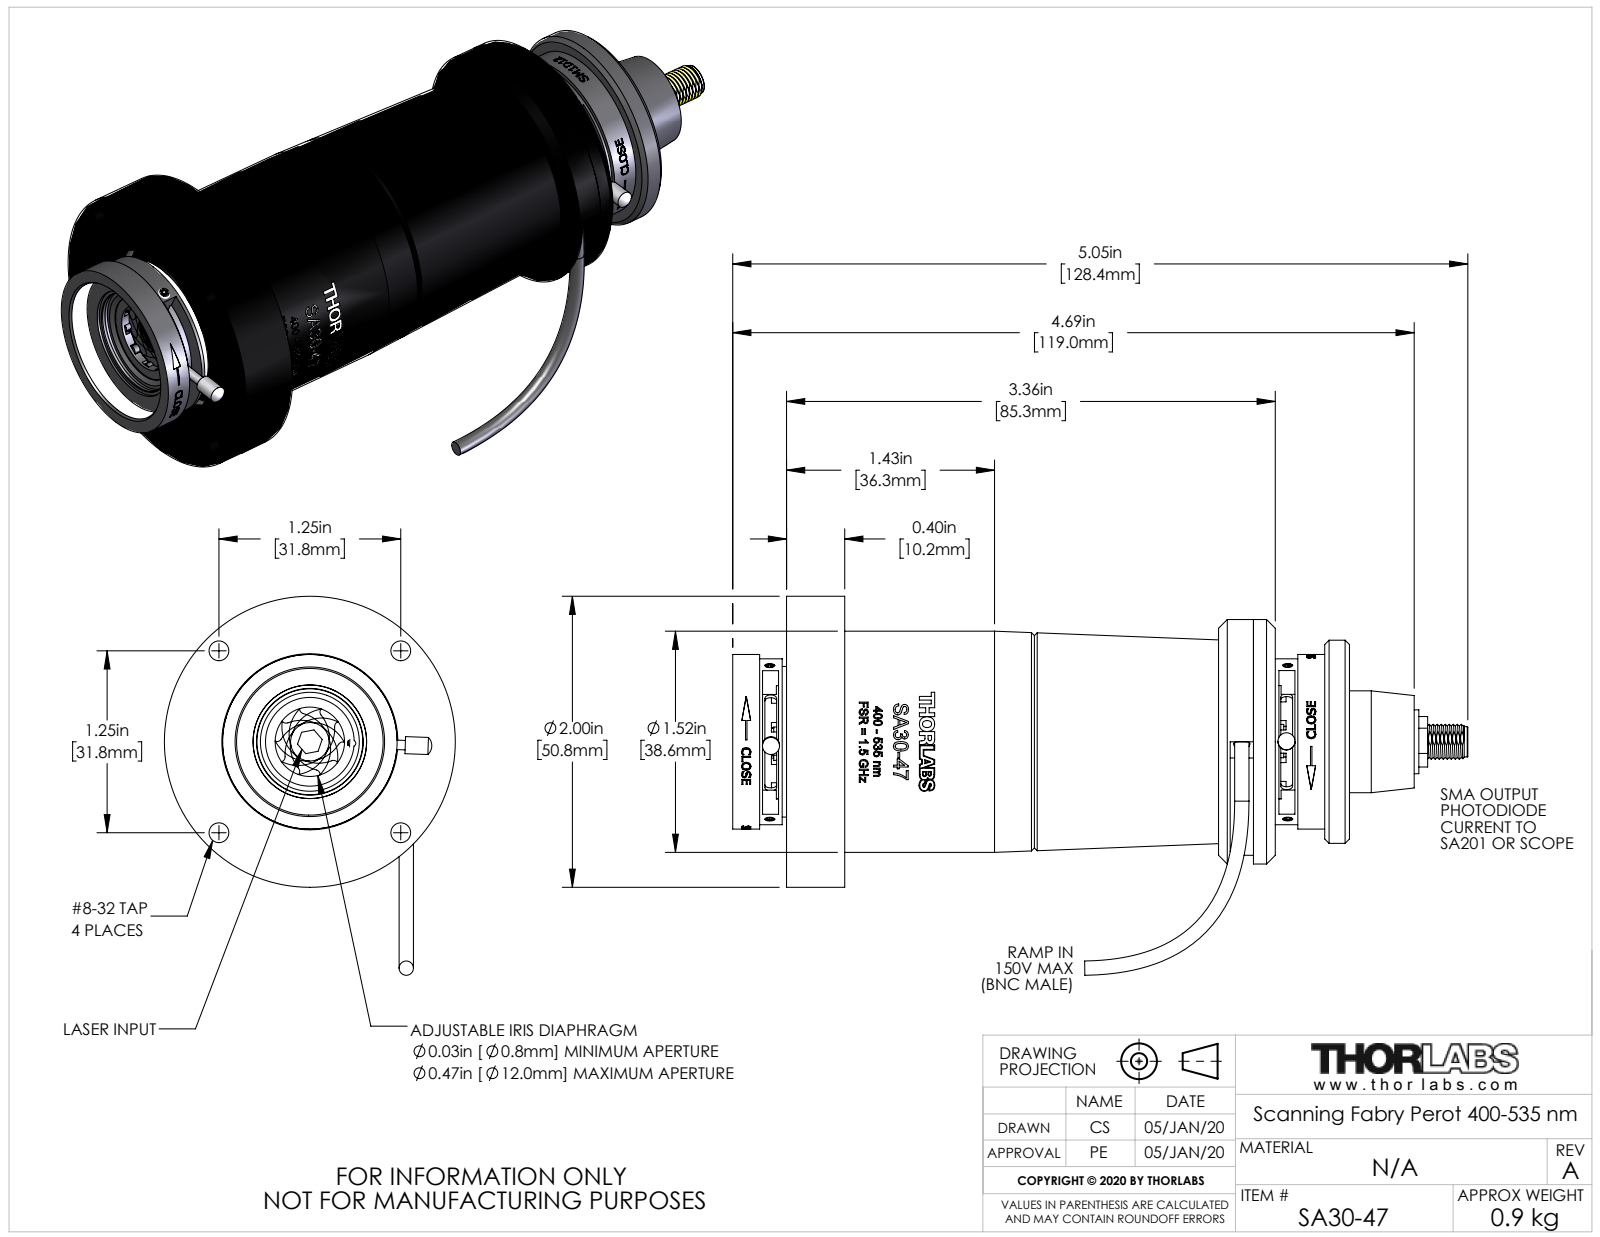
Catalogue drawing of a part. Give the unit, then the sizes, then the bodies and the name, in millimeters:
Units: millimetres
Overall size (bounding box): 128.37 × 66.16 × 50.8
Round holes (diameter × count): ⌀1.68 ×20, ⌀3.45 ×4, ⌀1.1 ×2, ⌀1.6 ×2, ⌀1 ×1, ⌀2.87 ×1, ⌀4.6 ×1, ⌀6.35 ×1, ⌀8.26 ×1, ⌀9.78 ×1, ⌀10.16 ×1, ⌀12.04 ×1
Round bosses / shafts (diameter × count): ⌀1.52 ×20, ⌀1.65 ×14, ⌀1.65 ×8, ⌀2.18 ×4, ⌀2.98 ×2, ⌀1.63 ×2, ⌀50.8 ×1, ⌀42.67 ×1
Partial cylindrical surfaces — rounded edges, fillets, slot ends (radius × count): R0.83 ×20, R0.85 ×20, R1.61 ×20, R6.38 ×20, R9.6 ×20, R0.62 ×2, R3.3 ×2, R25.4 ×2
Main face-to-face distances: 81.53, 3.81, 86.81, 12.96, 85.72, 1.14, 1.09, 85.67, 10.16, 71.37
Hole centre spacings: 8.72, 12, 4.58, 14.83, 4.86, 7.41, 7.42, 14.1
Volume: 54 584 mm³ · Surface area: 46 000 mm²
Bodies: 42 solids, 1575 faces (619 planar, 530 cylindrical, 426 other)
Part name (STEP PRODUCT): STN052122-E0W
STEP written by: SolidWorks 2018 (AUTOMOTIVE_DESIGN)
